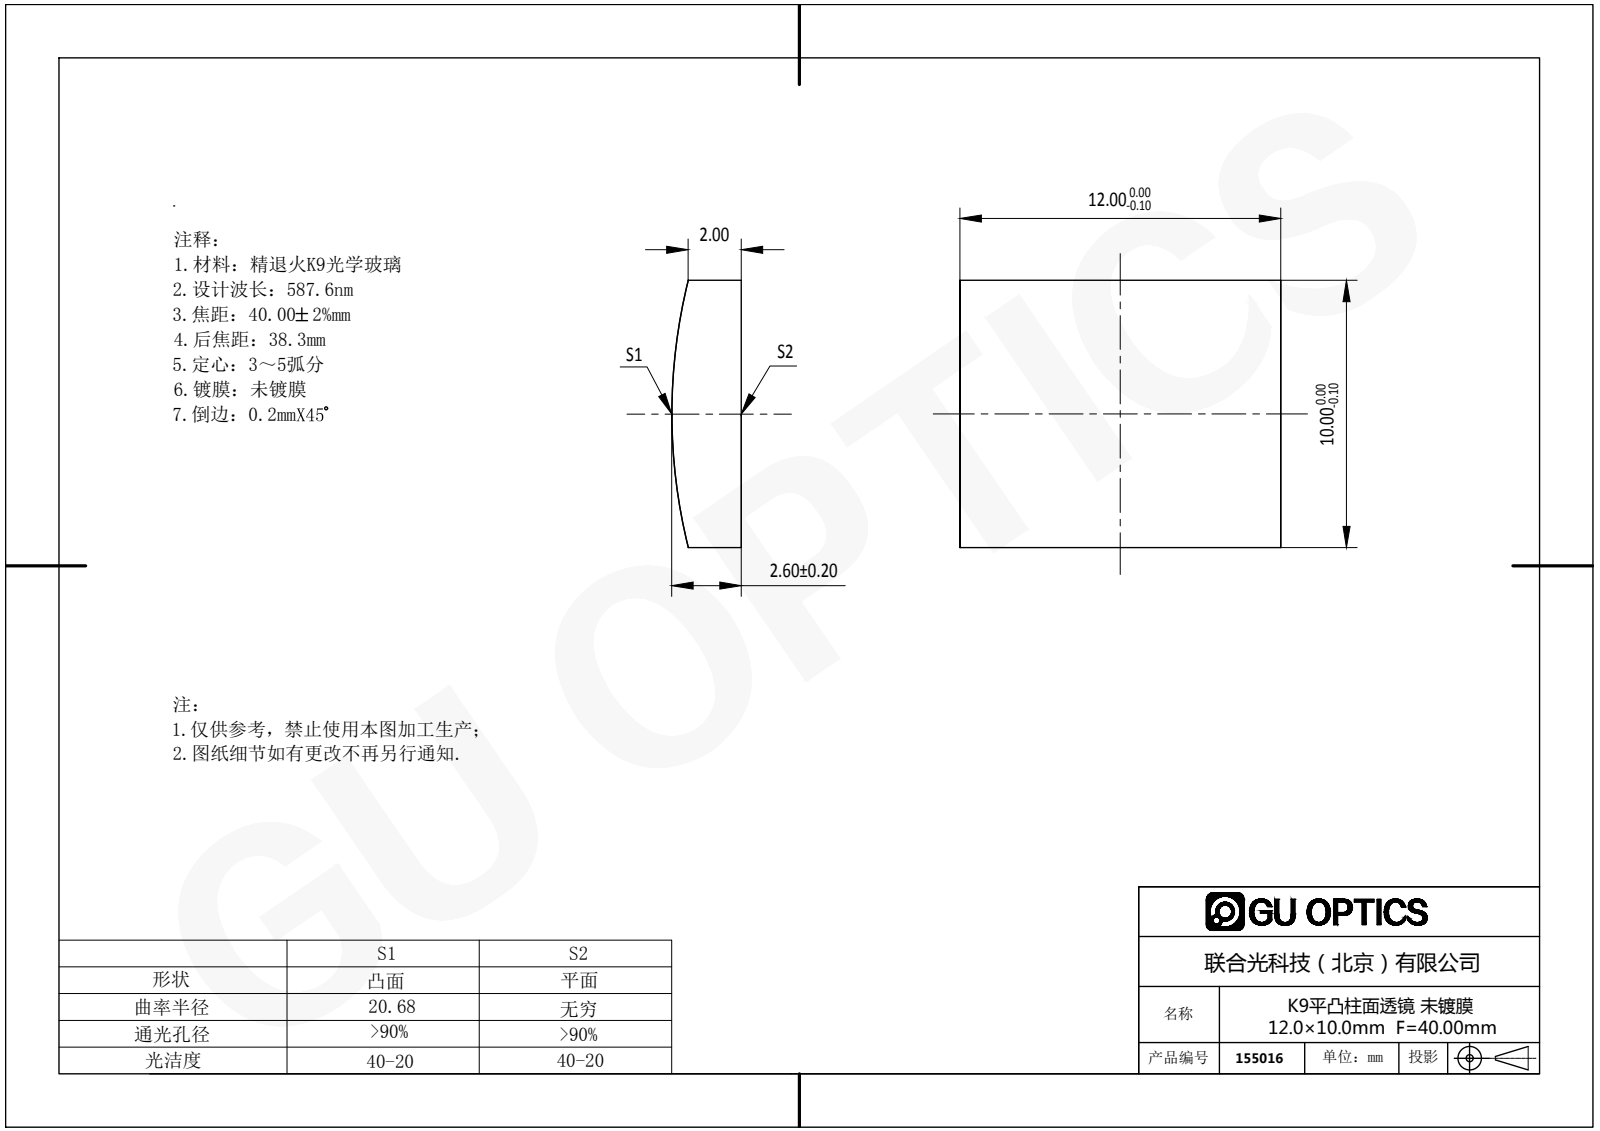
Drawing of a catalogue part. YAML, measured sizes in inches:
part_name: "155016"
step_written_by: "SolidWorks 2016 (AUTOMOTIVE_DESIGN)"
units: inches
bodies: {solids: 1, faces: 6, planar: 5, cylindrical: 1, other: 0}
overall_size: [0.472, 0.394, 0.102]
volume: 0.018
surface_area: 0.522
partial_cylinders:
  - {radius: 0.814, count: 1}
face_to_face_distances: [0.472, 0.394]
